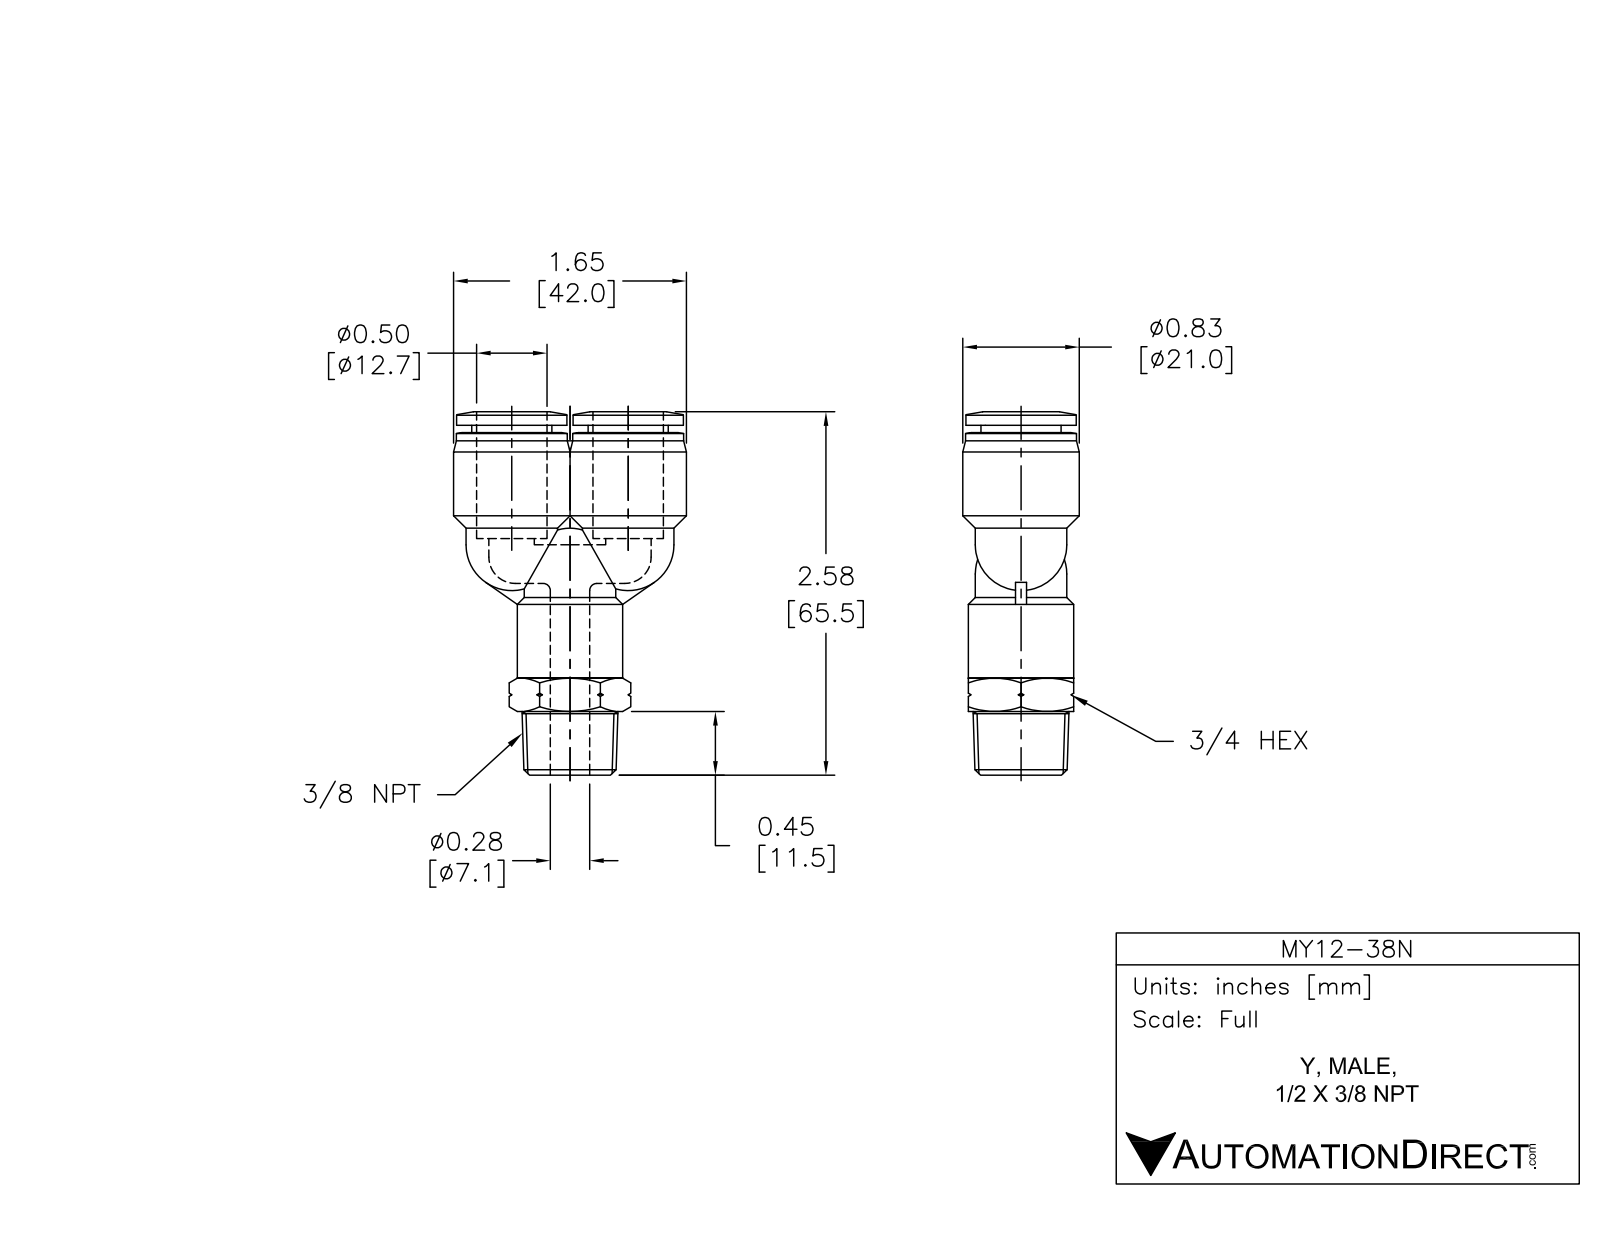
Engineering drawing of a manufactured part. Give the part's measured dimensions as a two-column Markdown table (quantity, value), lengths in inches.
| quantity | value |
| --- | --- |
| part name | MY12-38N |
| STEP written by | SolidWorks 2015 (AUTOMOTIVE_DESIGN) |
| units | inches |
| bodies | 1 solid, 121 faces (21 planar, 29 cylindrical, 71 other) |
| overall size | 2.581 × 1.654 × 0.827 |
| volume | 1.161 in³ |
| surface area | 15.87 in² |
| round holes (diameter × count) | 0.51 × 2, 0.276 × 1 |
| round bosses / shafts (diameter × count) | 0.65 × 3, 0.827 × 2, 0.787 × 2, 0.783 × 2, 0.569 × 2, 0.748 × 1 |
| main face-to-face distances | 0.809, 0.758, 0.051, 0.748, 1.675, 2.433, 2.484, 0.453, 1.222, 1.98 |
| hole center spacings | 0.413, 0.827 |
